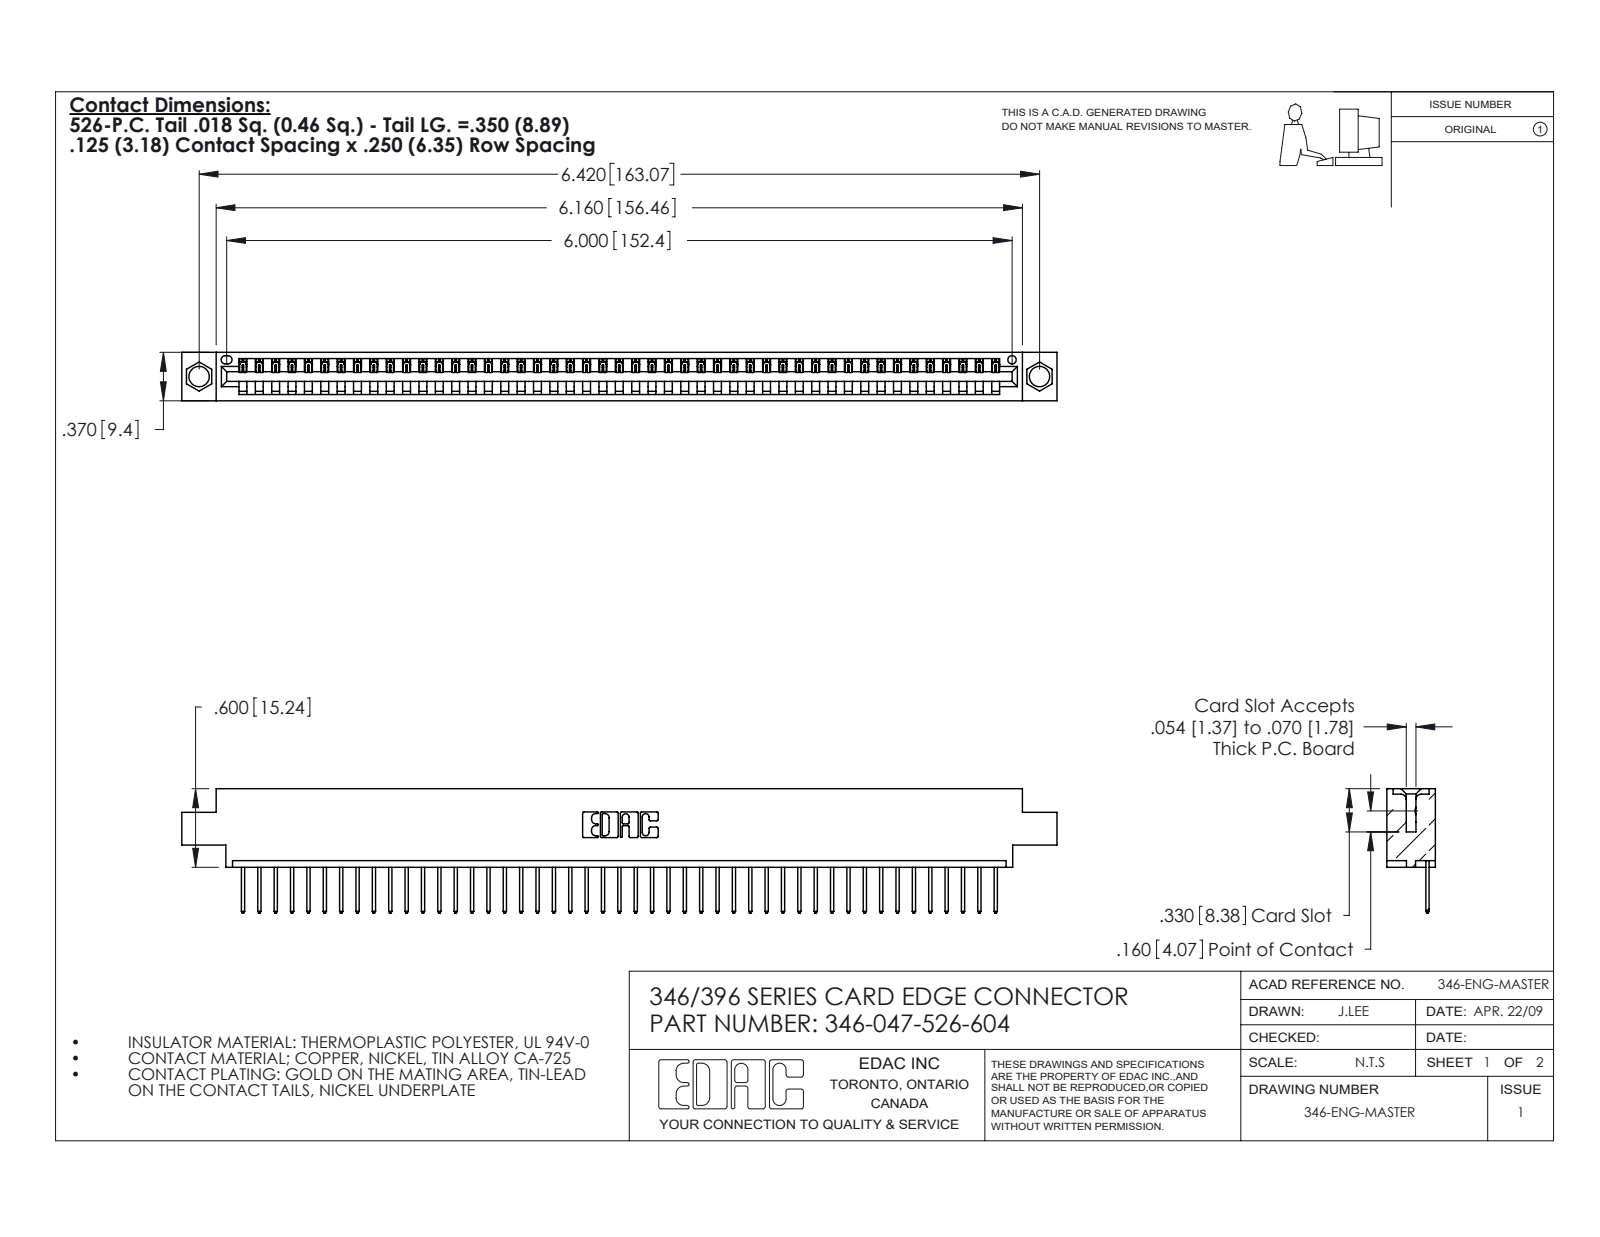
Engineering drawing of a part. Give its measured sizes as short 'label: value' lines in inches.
name: 346-047-526-604; 345-292-001_345-293-126; 346 Part_0.170 Offset - 0.156 Dia-TH
written by: SolidWorks 2020 (CONFIG_CONTROL_DESIGN)
unit: in
bodies: 48 solids, 2866 faces (1974 planar, 892 cylindrical, 0 other)
size: 6.685 × 0.95 × 0.37
volume: 0.976 in³; area: 30.99 in²
holes: 2× ⌀0.156, 1× ⌀0.064
rounds: 94× R0.006, 94× R0.01, 22× R0.01, 6× R0.007, 6× R0.031, 3× R0.026, 2× R0.031, 2× R0.04
face distances: 0.048, 0.322, 0.37, 0.25, 0.072, 0.298, 0.025, 0.222, 0.148, 0.1
hole spacings: 0.246, 6.211, 6.42
